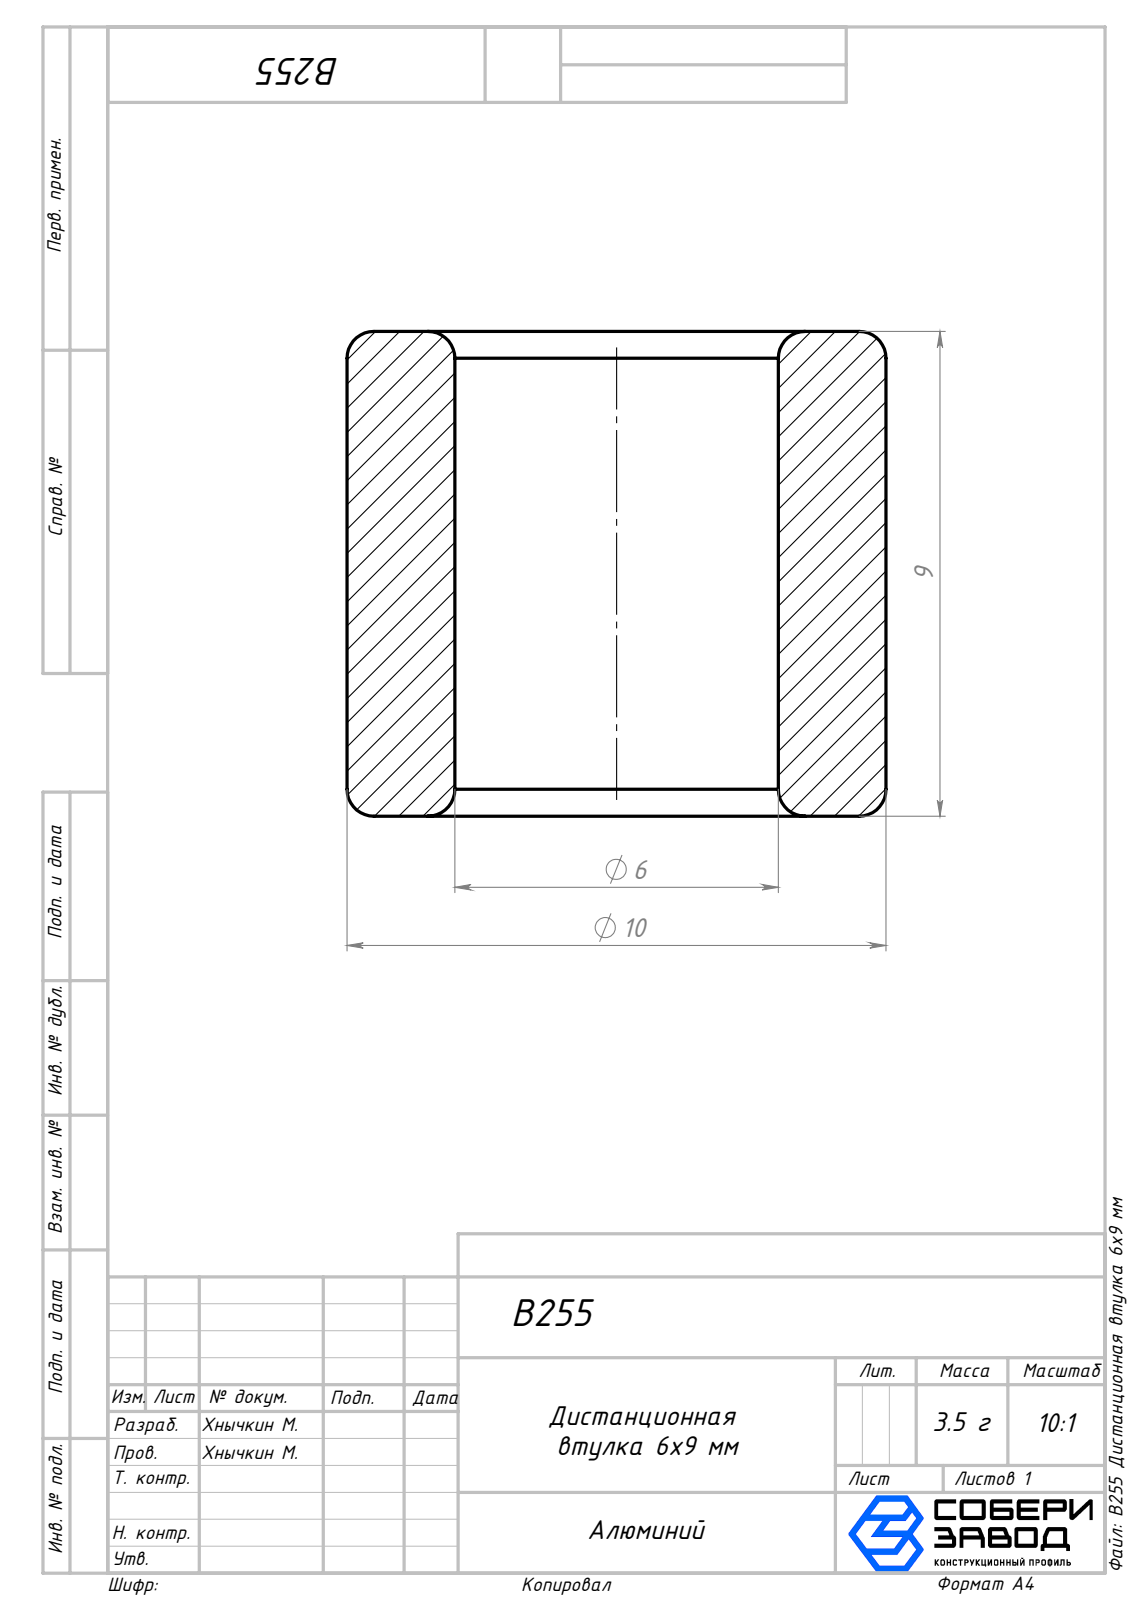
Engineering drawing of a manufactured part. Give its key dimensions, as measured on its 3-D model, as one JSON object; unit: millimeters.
{"part_name": "B255 Дистанционная втулка 6x9 мм", "step_written_by": "SolidWorks 2026 (AUTOMOTIVE_DESIGN)", "units": "millimeters", "bodies": {"solids": 1, "faces": 14, "planar": 2, "cylindrical": 4, "other": 8}, "overall_size": [10, 10, 9], "volume_mm3": 447, "surface_area_mm2": 531, "round_holes": [[6, 1]], "round_bosses_or_shafts": [[10, 1]], "face_to_face_distances": [9]}
